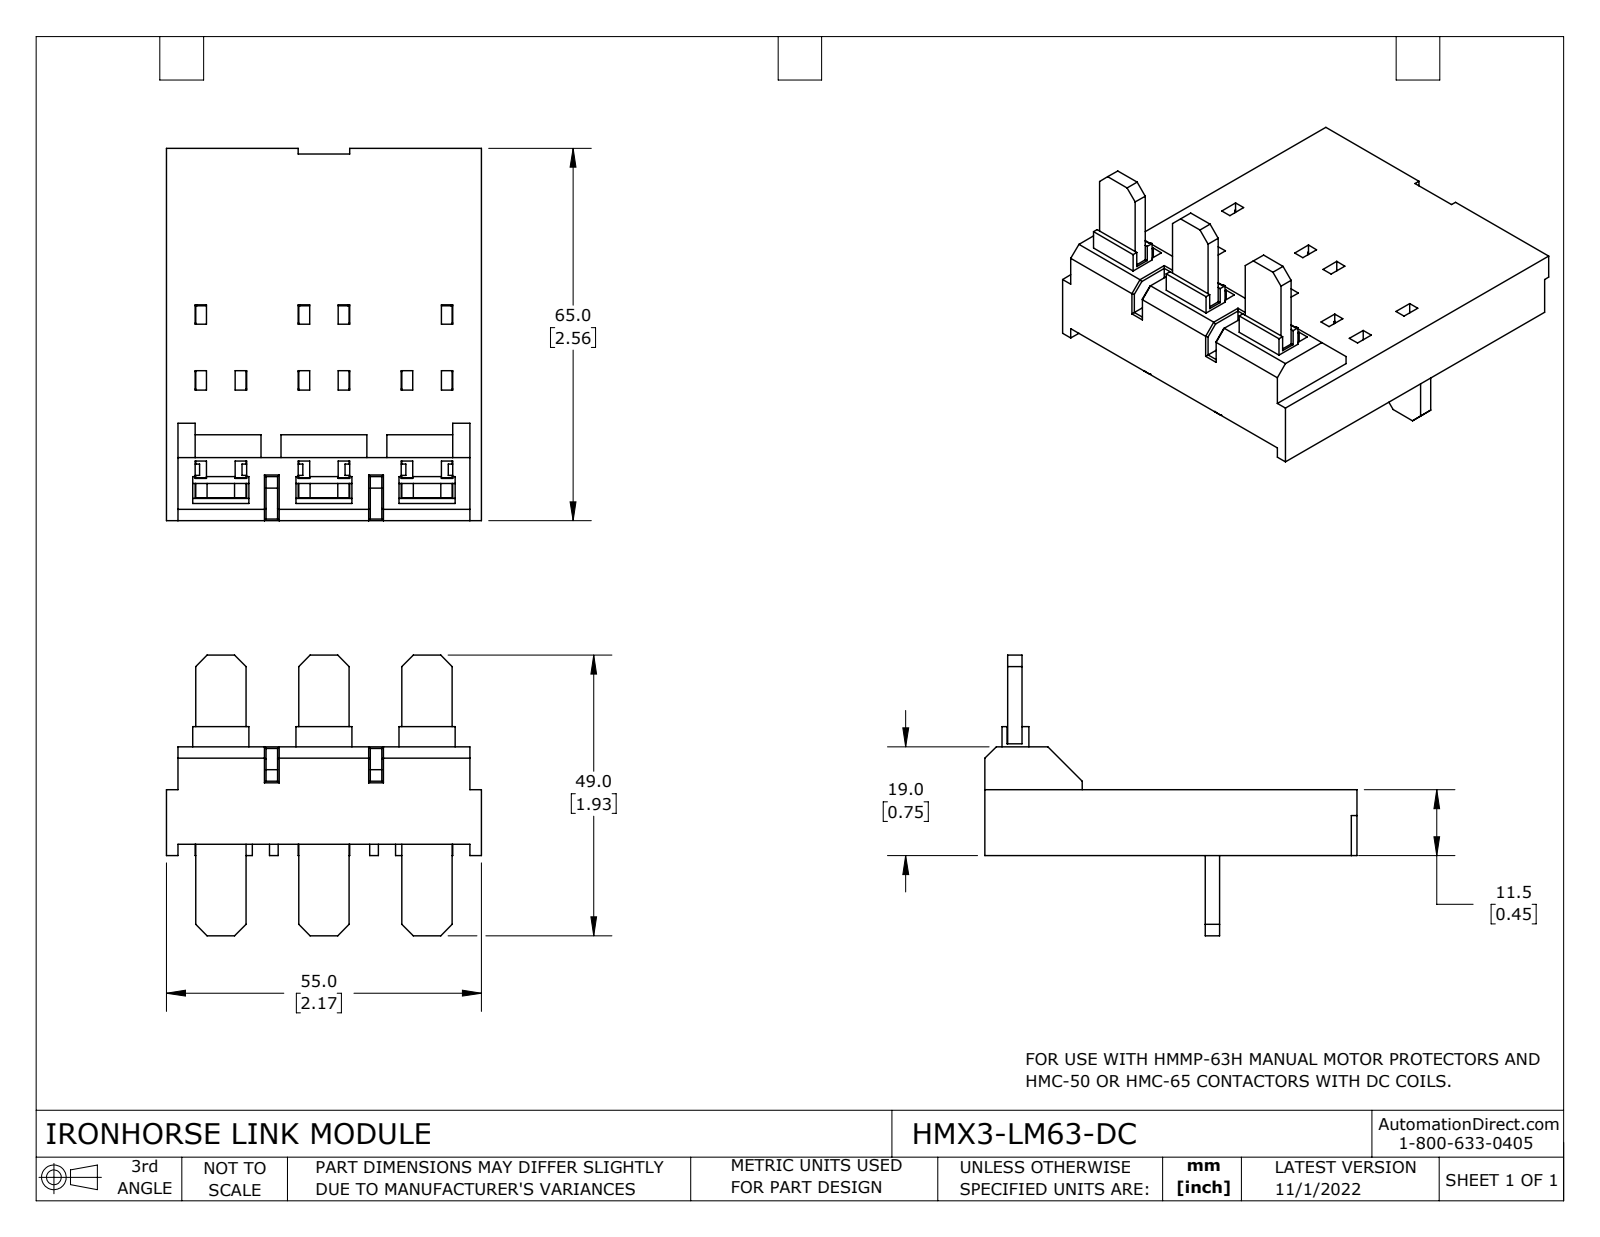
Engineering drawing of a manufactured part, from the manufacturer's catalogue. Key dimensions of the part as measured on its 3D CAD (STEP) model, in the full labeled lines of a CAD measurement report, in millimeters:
Part name (STEP PRODUCT): HMX3-LM63-DC
STEP written by: SolidWorks 2021 (CONFIG_CONTROL_DESIGN)
Units: millimetres
Bodies: 1 solid, 773 faces (753 planar, 20 cylindrical, 0 other)
Overall size (bounding box): 65 × 55 × 49
Volume: 21 250 mm³ · Surface area: 21 720 mm²
Partial cylindrical surfaces — rounded edges, fillets, slot ends (radius × count): R1 ×3, R3.5 ×3, R2 ×1
Main face-to-face distances: 2, 2.5, 18, 35, 37, 4.5, 4, 16, 53, 3
